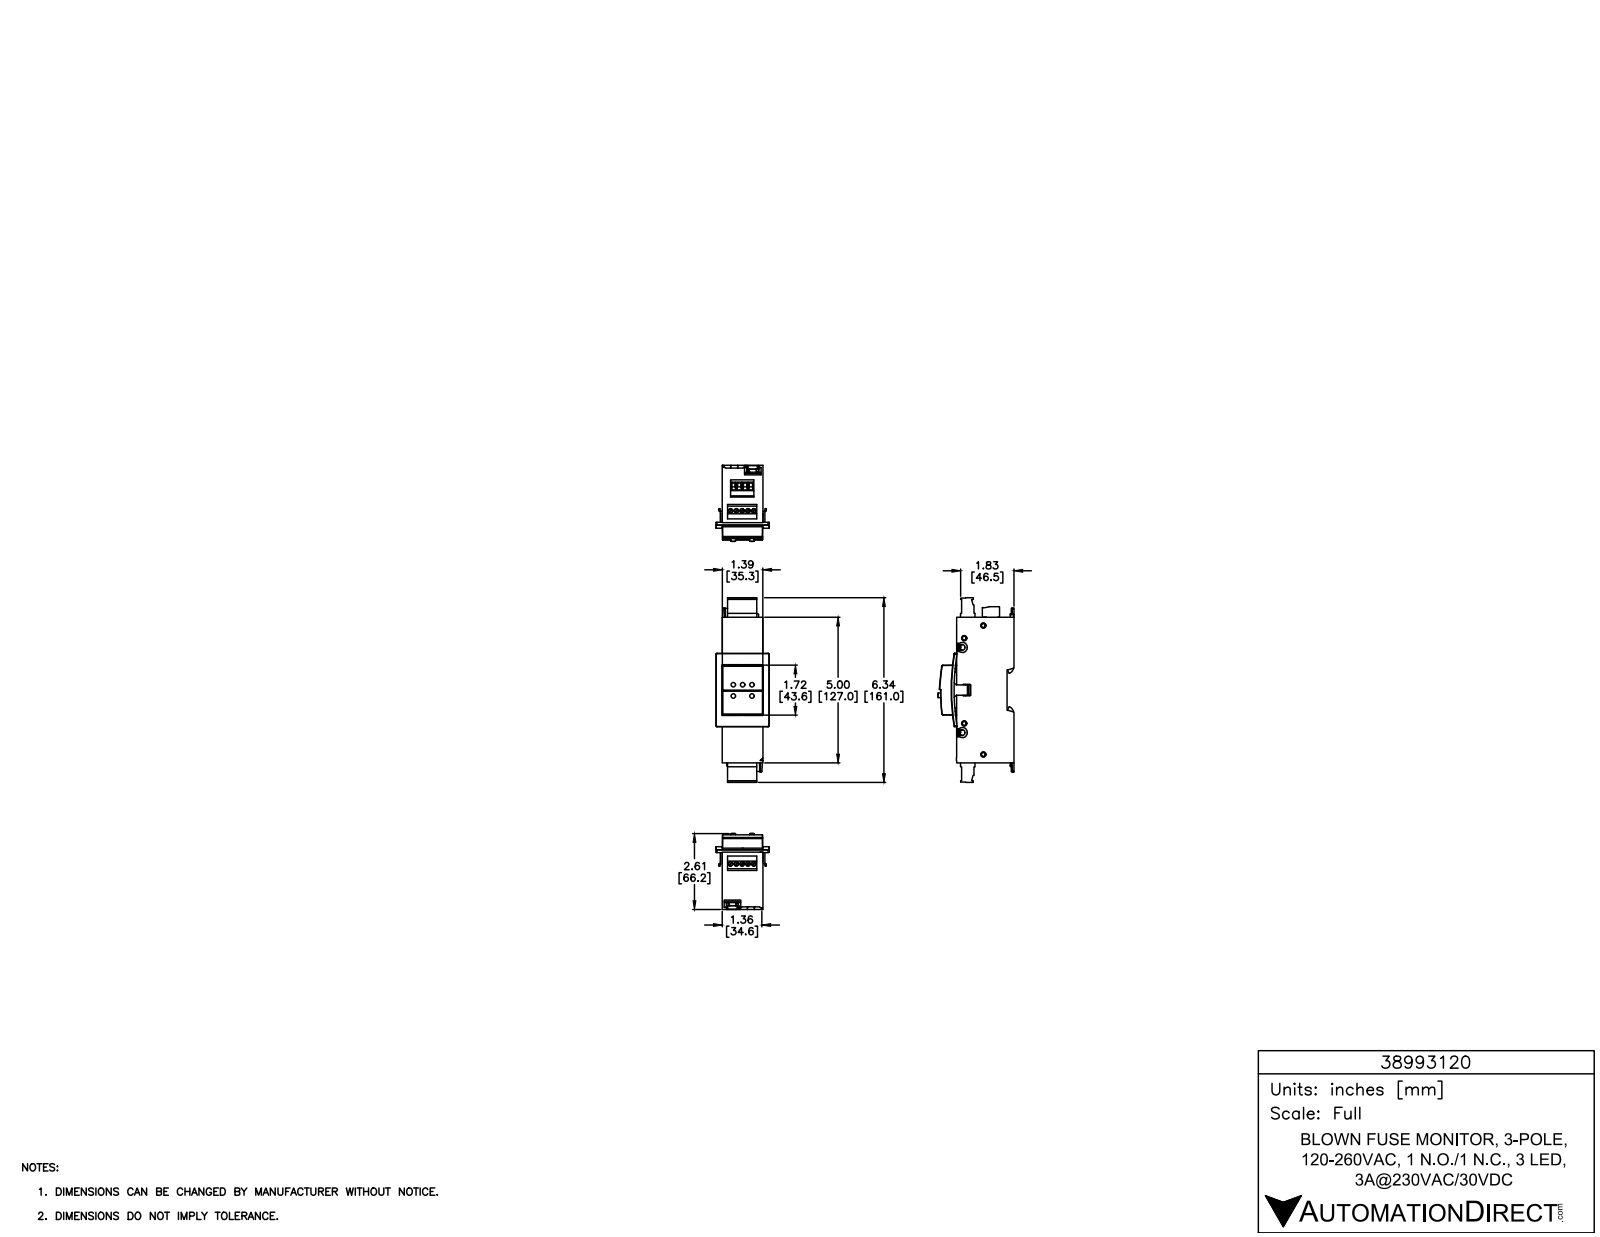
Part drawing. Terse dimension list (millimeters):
name: 38993120
written by: SolidWorks 2015 (AUTOMOTIVE_DESIGN)
unit: mm
bodies: 1 solid, 847 faces (521 planar, 248 cylindrical, 78 other)
size: 161 × 66.4 × 46.5
volume: 243 300 mm³; area: 44 520 mm²
holes: 9× ⌀4, 4× ⌀4.6, 2× ⌀4.2
bosses: 9× ⌀3.8, 4× ⌀4.2
rounds: 24× R0.2, 24× R0.2, 24× R0.6, 15× R1, 12× R0.3, 10× R0.5, 4× R1.2, 4× R1.5
face distances: 35.5, 44, 50, 6, 127, 17.8, 10.2, 5.4, 4.3, 39.7
hole spacings: 5.1, 10.2, 15.2, 9.8, 20.1, 20.3, 31.9, 62.7
